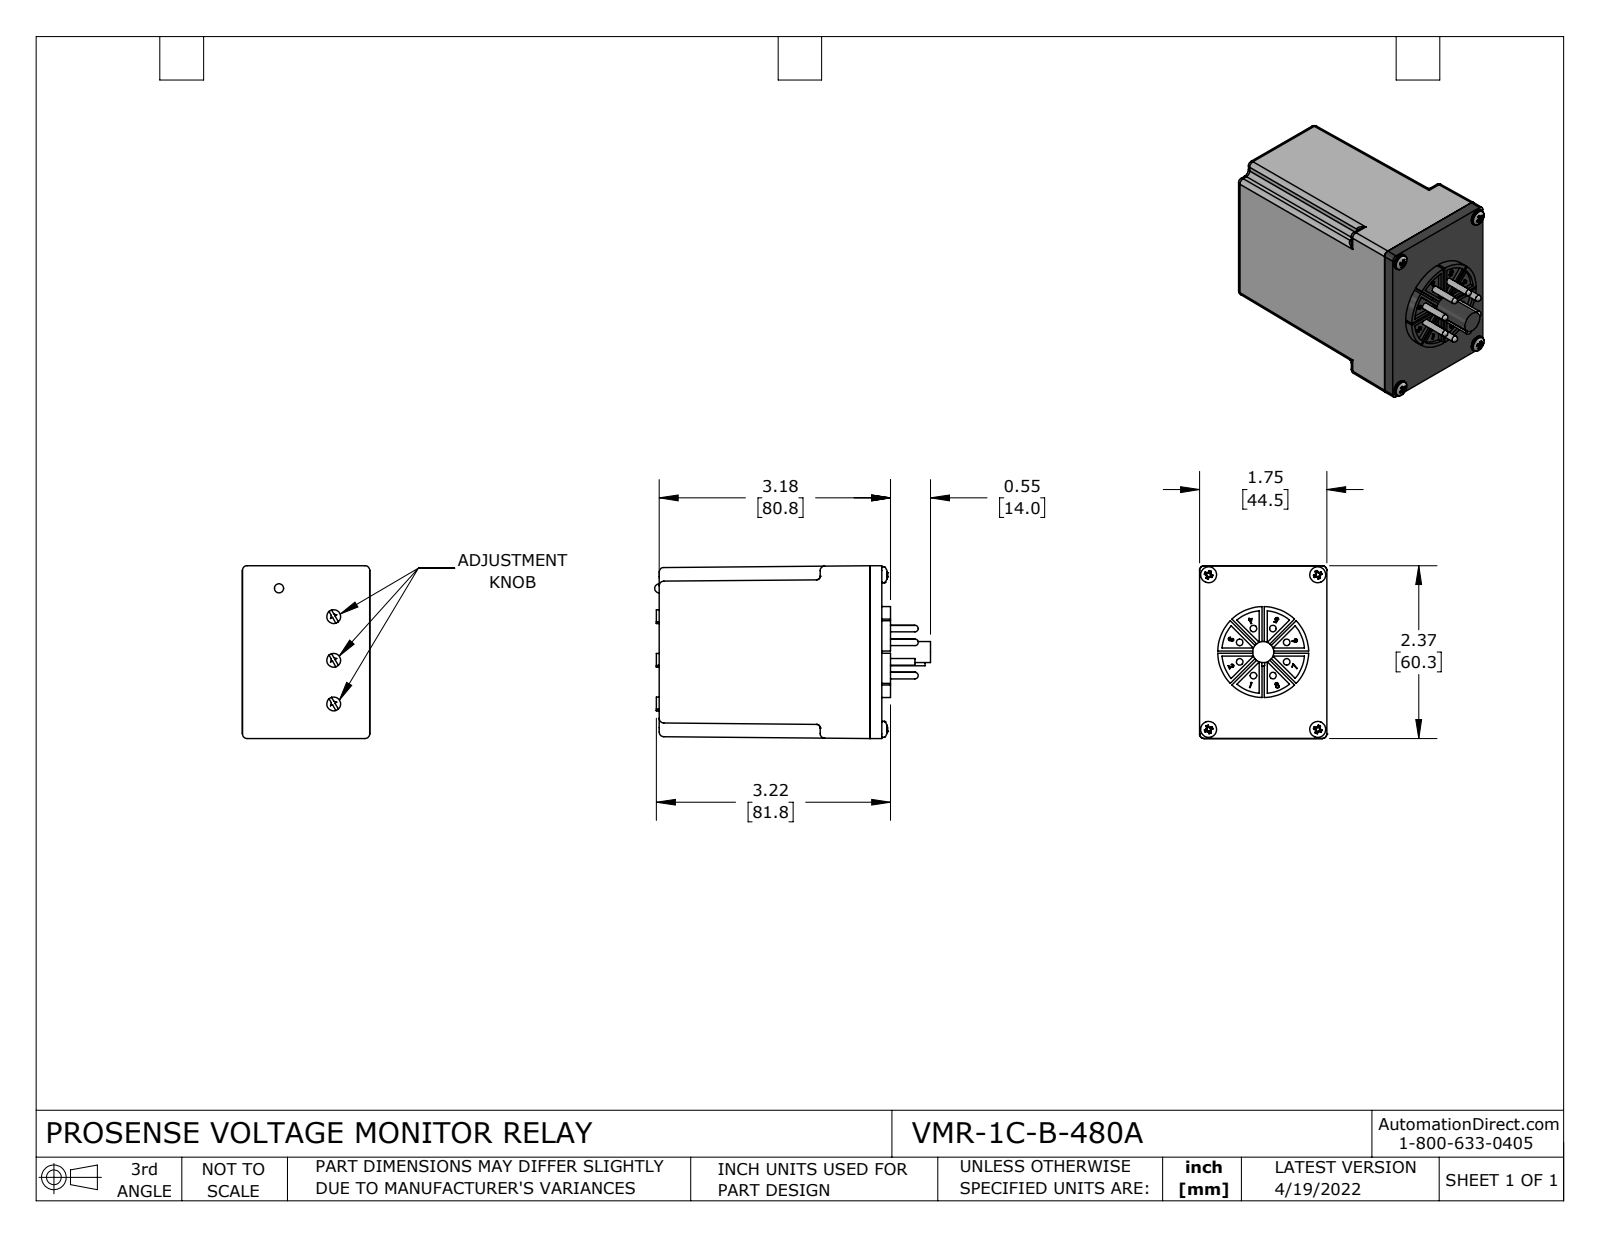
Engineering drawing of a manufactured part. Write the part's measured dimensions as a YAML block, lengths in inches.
part_name: "VMR-1C-B-480A"
step_written_by: "SolidWorks 2021 (CONFIG_CONTROL_DESIGN)"
units: inches
bodies: {solids: 18, faces: 574, planar: 249, cylindrical: 170, other: 155}
overall_size: [3.79, 2.375, 1.75]
volume: 12.25
surface_area: 44.71
round_holes:
  - {diameter: 0.125, count: 4}
round_bosses_or_shafts:
  - {diameter: 0.09, count: 8}
  - {diameter: 0.219, count: 4}
  - {diameter: 0.19, count: 3}
  - {diameter: 1.25, count: 1}
  - {diameter: 0.29, count: 1}
partial_cylinders:
  - {radius: 0.063, count: 32}
  - {radius: 0.005, count: 8}
  - {radius: 0.05, count: 4}
  - {radius: 0.57, count: 1}
face_to_face_distances: [2.9, 0.16, 3.06, 0.07, 0.23, 3.13, 0.188, 0.05, 0.12, 0.28]
hole_center_spacings: [1.5, 2.125, 2.601]
